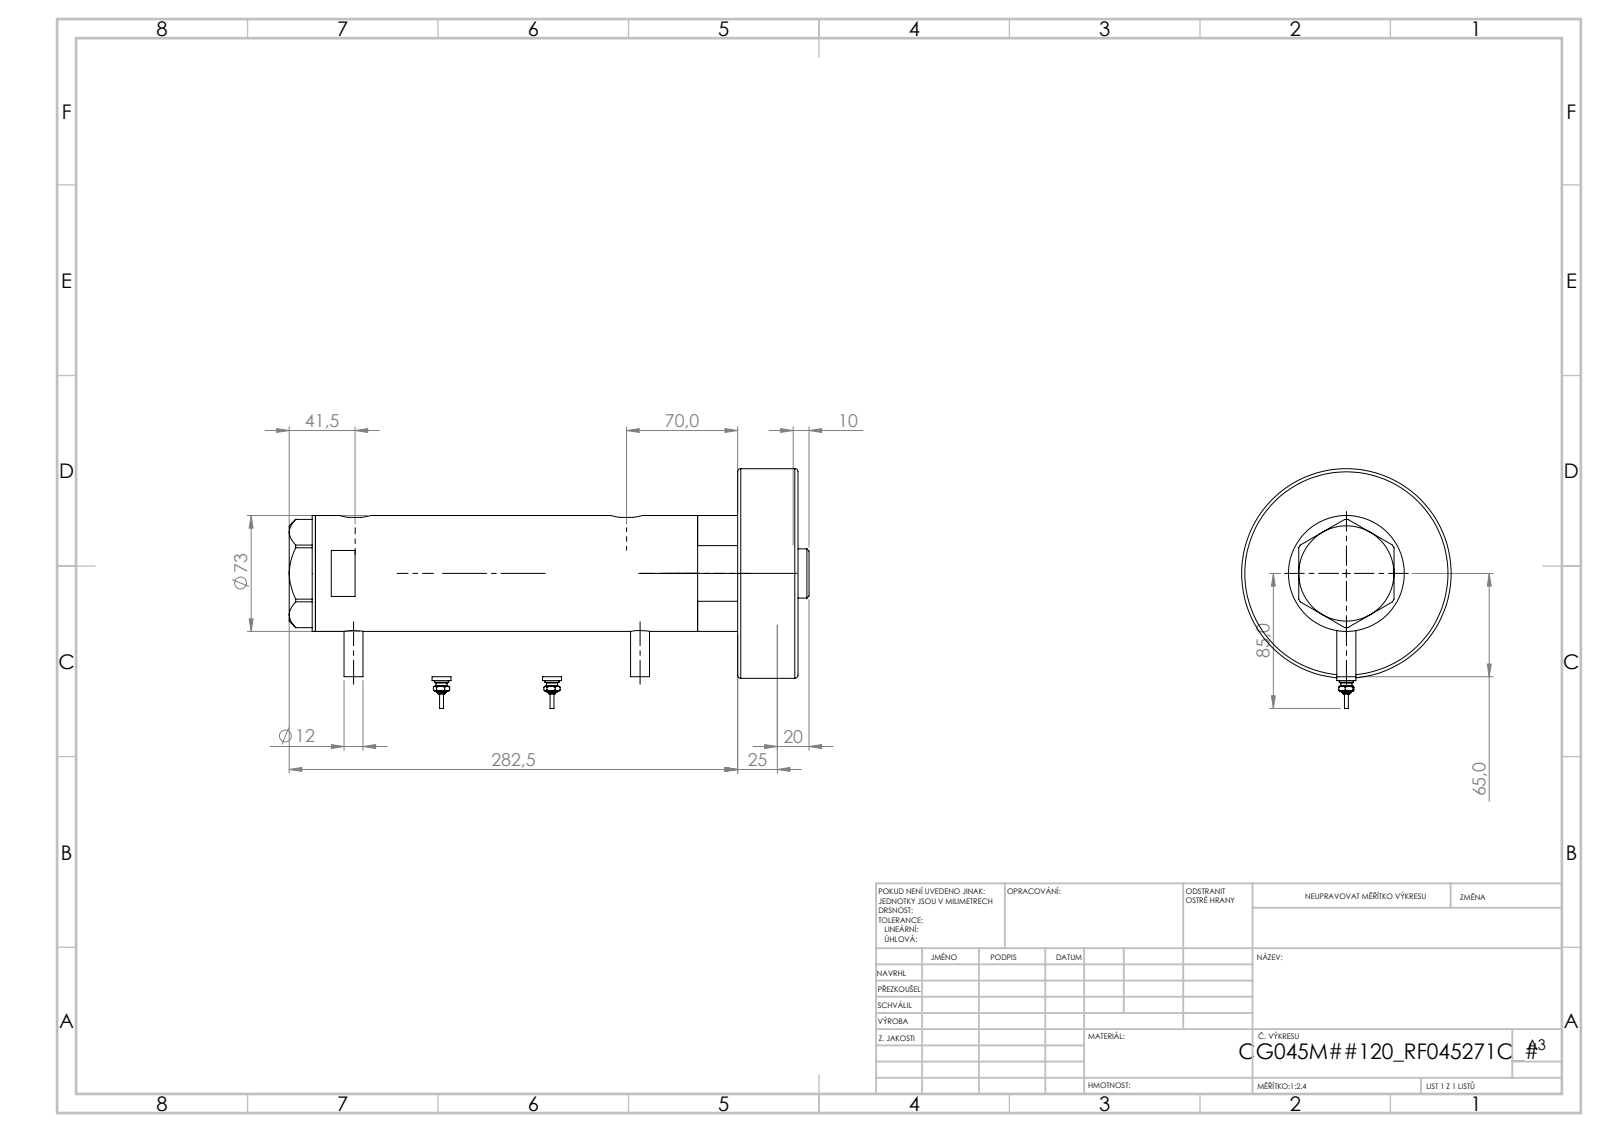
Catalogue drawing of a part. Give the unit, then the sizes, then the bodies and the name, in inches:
Units: inches
Overall size (bounding box): 12.265 × 5.307 × 5.197
Round holes (diameter × count): ⌀0.197 ×2, ⌀0.492 ×2, ⌀0.518 ×2, ⌀0.413 ×1, ⌀1.26 ×1, ⌀1.319 ×1, ⌀1.772 ×1, ⌀1.89 ×1, ⌀2.362 ×1, ⌀2.52 ×1
Round bosses / shafts (diameter × count): ⌀0.472 ×3, ⌀0.354 ×2, ⌀0.276 ×2, ⌀0.171 ×2, ⌀0.094 ×2, ⌀5.197 ×1, ⌀2.874 ×1, ⌀2.283 ×1
Partial cylindrical surfaces — rounded edges, fillets, slot ends (radius × count): R0.394 ×2
Main face-to-face distances: 1.496, 9.742, 11.238, 7.368, 2.374, 3.87, 1.024, 6.344, 8.719, 10.215
Hole centre spacings: 6.758, 0.039, 0.039, 0.335, 0.335, 6.384, 6.423, 6.423
Volume: 90.86 in³ · Surface area: 344.7 in²
Bodies: 7 solids, 241 faces (80 planar, 83 cylindrical, 78 other)
Part name (STEP PRODUCT): V270CG_BACK; V270CG_MIDDLE; V270CG_FRONT; V270CG_VC (+2 more)
STEP written by: SolidWorks 2019 (CONFIG_CONTROL_DESIGN)
